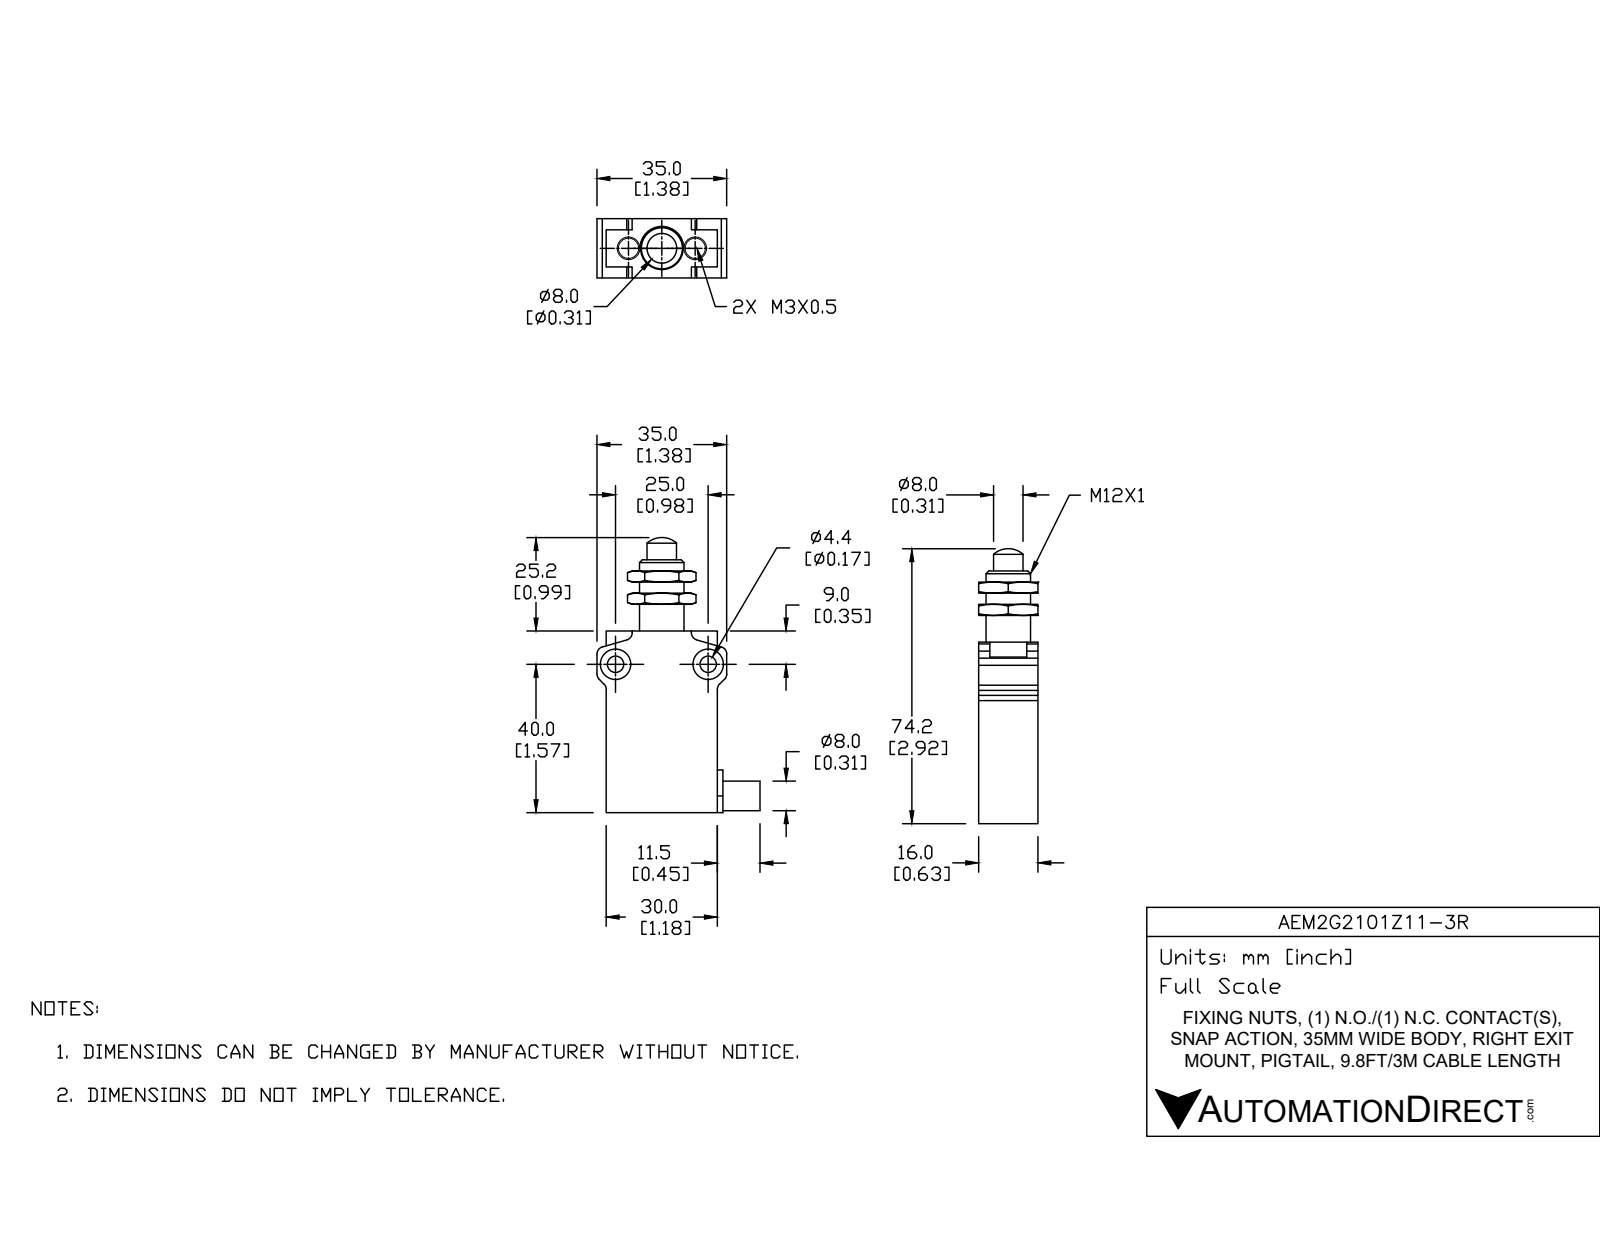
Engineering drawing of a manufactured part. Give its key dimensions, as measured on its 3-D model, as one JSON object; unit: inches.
{"part_name": "AEM2G2101Z11-3R", "step_written_by": "SolidWorks 2017 (AUTOMOTIVE_DESIGN)", "units": "inches", "bodies": {"solids": 6, "faces": 147, "planar": 63, "cylindrical": 48, "other": 36}, "overall_size": [2.92, 1.87, 0.676], "volume_in3": 1.613, "surface_area_in2": 15.97, "round_holes": [[0.118, 2], [0.173, 2], [0.323, 2], [0.317, 1], [0.472, 1]], "round_bosses_or_shafts": [[0.323, 1], [0.313, 1]], "partial_cylinders_radius": [[0.079, 8], [0.256, 1]], "face_to_face_distances": [0.63, 1.181, 0.118, 0.472, 0.236, 1.929, 0.354, 1.74, 0.189, 0.591], "hole_center_spacings": [0.374, 0.748, 0.984]}
